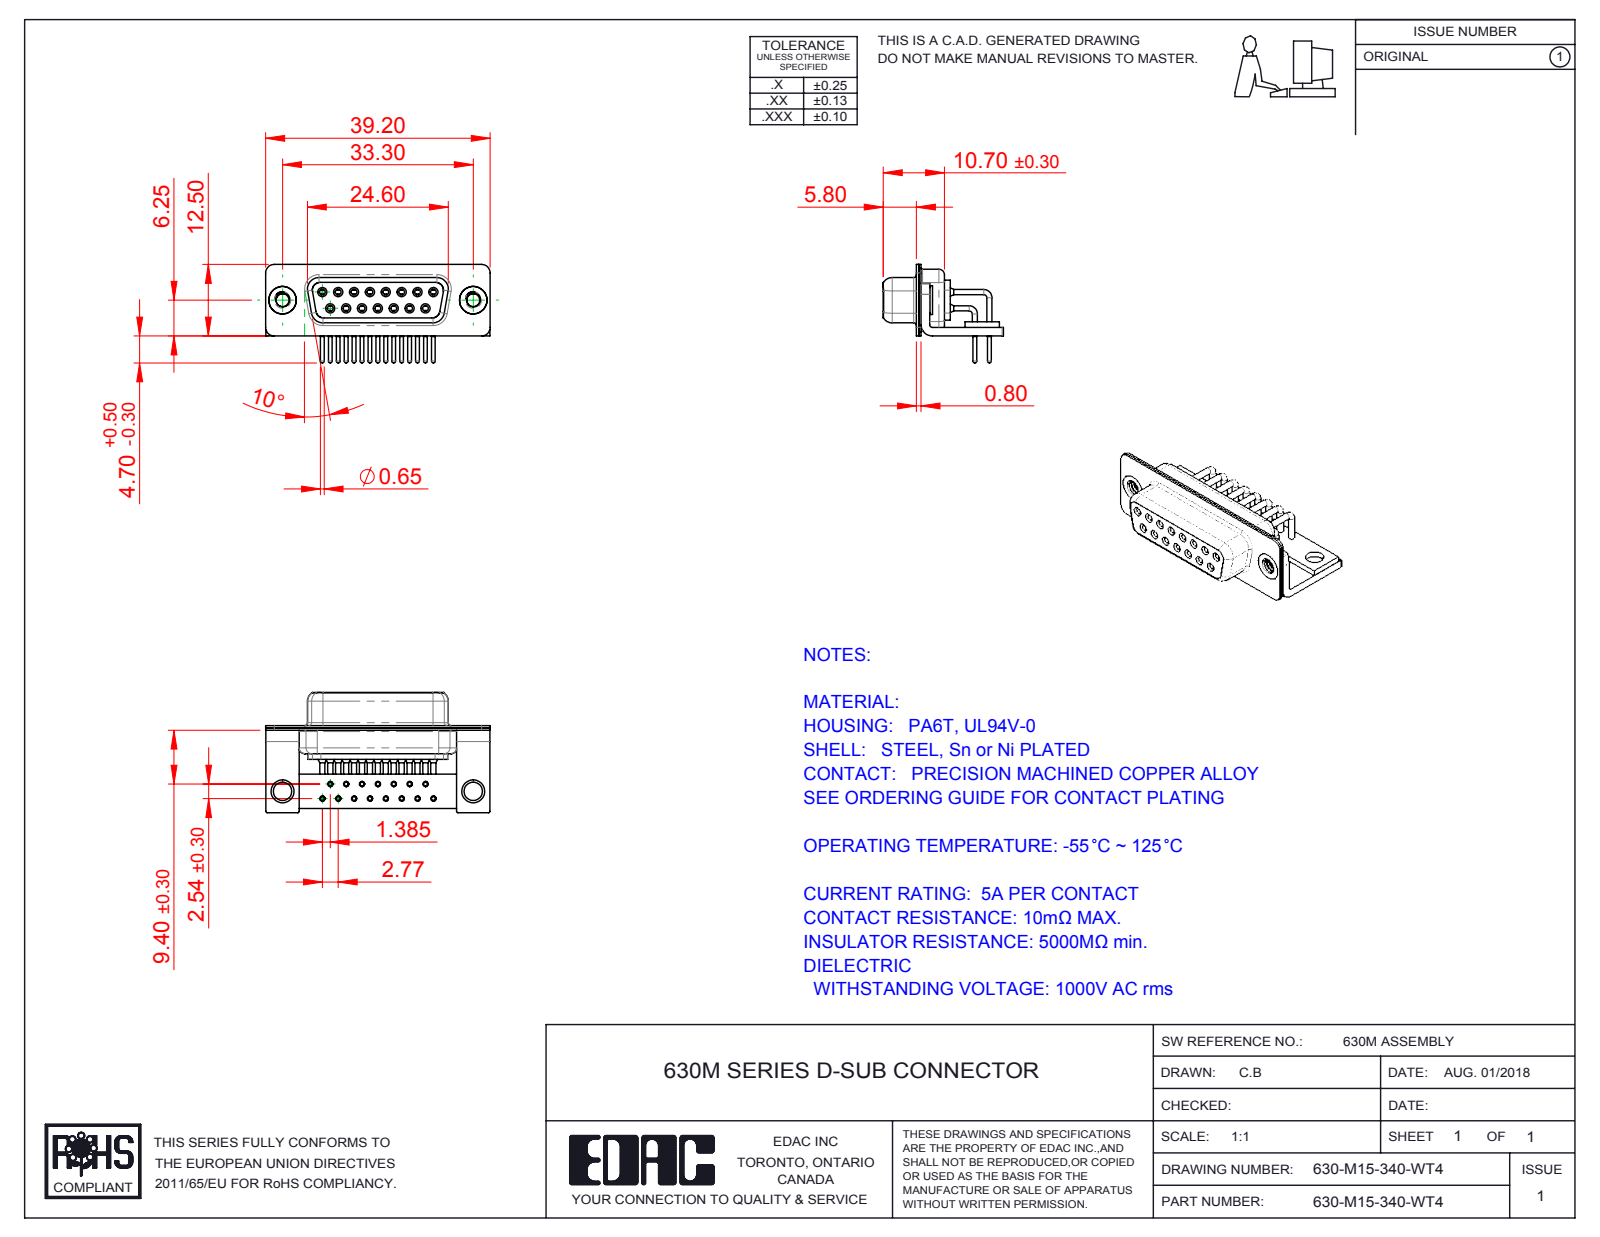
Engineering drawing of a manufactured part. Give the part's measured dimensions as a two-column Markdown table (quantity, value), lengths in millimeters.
| quantity | value |
| --- | --- |
| part name | 630M Stabilizer Bracket; 630M Housing_15 Contacts; 630M 4-40 Threaded Rivet_Stabilizer; 630M Shell Front_15 Contacts (+5 more) |
| STEP written by | SolidWorks 2016 (CONFIG_CONTROL_DESIGN) |
| units | millimeters |
| bodies | 23 solids, 1154 faces (318 planar, 534 cylindrical, 302 other) |
| overall size | 39.2 × 21 × 17.2 |
| volume | 3 044 mm³ |
| surface area | 7 715 mm² |
| round holes (diameter × count) | 0.9 × 15, 1 × 15, 1.1 × 15, 1.7 × 15, 1.8 × 15, 2 × 15, 2.26 × 2, 3.2 × 2, 4 × 2, 4.8 × 2 |
| round bosses / shafts (diameter × count) | 0.9 × 27, 1.6 × 15, 1.5 × 15, 0.65 × 15, 5 × 2, 4.9 × 2 |
| partial cylindrical surfaces (radius × count) | 0.25 × 16, 1.5 × 16, 2 × 13, 1.35 × 8, 1.6 × 8, 0.5 × 5, 0.6 × 4, 0.65 × 4 |
| main face-to-face distances | 0.4, 0.8, 2.3, 9.35, 1.9, 1.5, 1, 1.45, 8.95, 0.85 |
| hole center spacings | 2.77, 5.54, 8.31, 3.16, 4.87, 11.08, 2.89, 7.37 |
